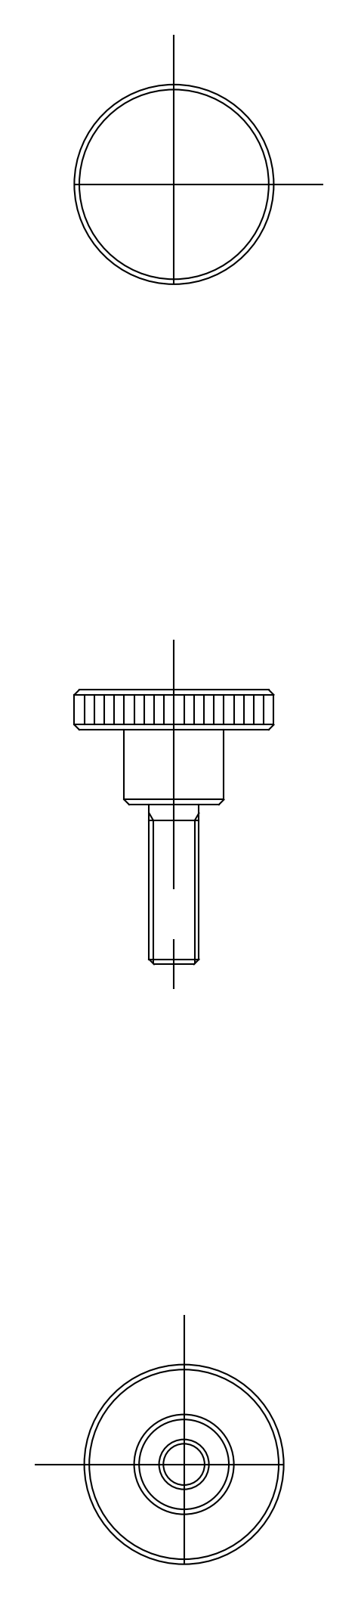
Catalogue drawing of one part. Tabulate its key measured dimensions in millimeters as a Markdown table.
| quantity | value |
| --- | --- |
| part name | knob |
| STEP written by | CADfix (AUTOMOTIVE_DESIGN) |
| units | millimeters |
| bodies | 1 solid, 18 faces (0 planar, 0 cylindrical, 18 other) |
| overall size | 27.5 × 20 × 20 |
| volume | 2 143 mm³ |
| surface area | 1 315 mm² |
